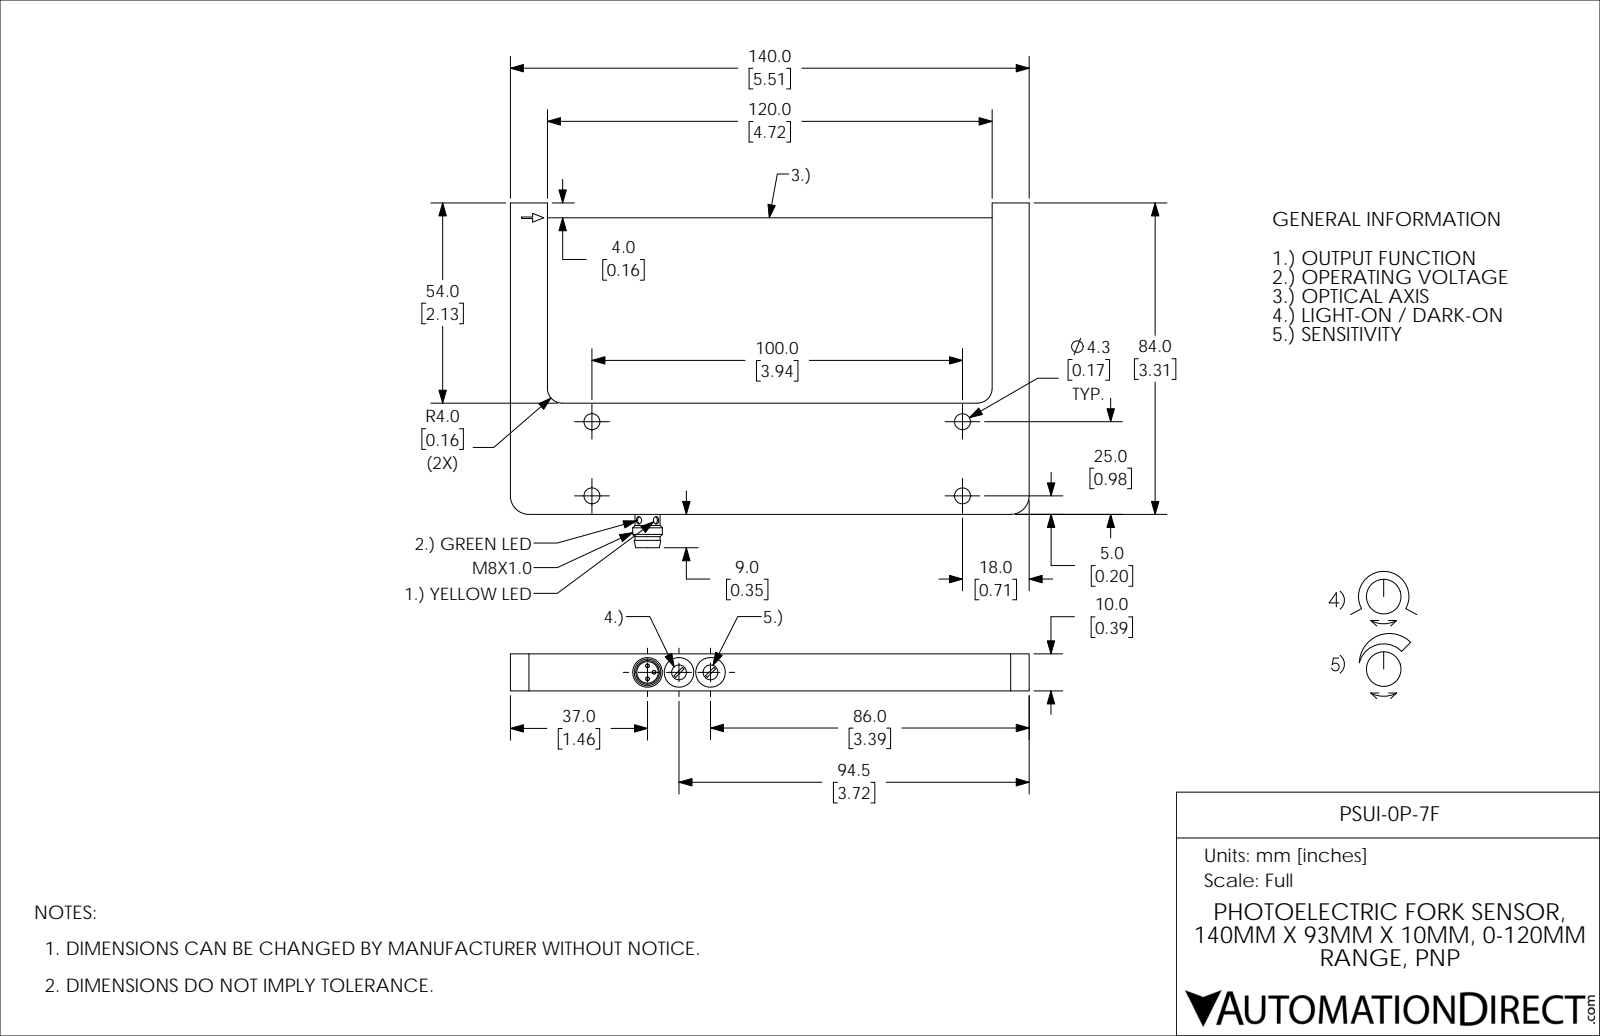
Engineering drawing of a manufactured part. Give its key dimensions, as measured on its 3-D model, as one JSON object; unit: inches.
{"part_name": "PSUI-0P-7F", "step_written_by": "SolidWorks 2017 (AUTOMOTIVE_DESIGN)", "units": "inches", "bodies": {"solids": 1, "faces": 68, "planar": 35, "cylindrical": 27, "other": 6}, "overall_size": [5.512, 3.661, 0.394], "volume_in3": 3.197, "surface_area_in2": 26.09, "round_holes": [[0.169, 4], [0.079, 2], [0.157, 2], [0.315, 2], [0.228, 1]], "round_bosses_or_shafts": [[0.039, 3], [0.315, 1], [0.267, 1]], "partial_cylinders_radius": [[0.063, 2], [0.157, 2], [0.197, 2]], "face_to_face_distances": [0.394, 1.181, 5.118, 5.512, 4.724, 2.126, 3.307, 3.303, 1.177, 0.157], "hole_center_spacings": [0.335, 0.787, 3.937, 4.015, 0.669]}
